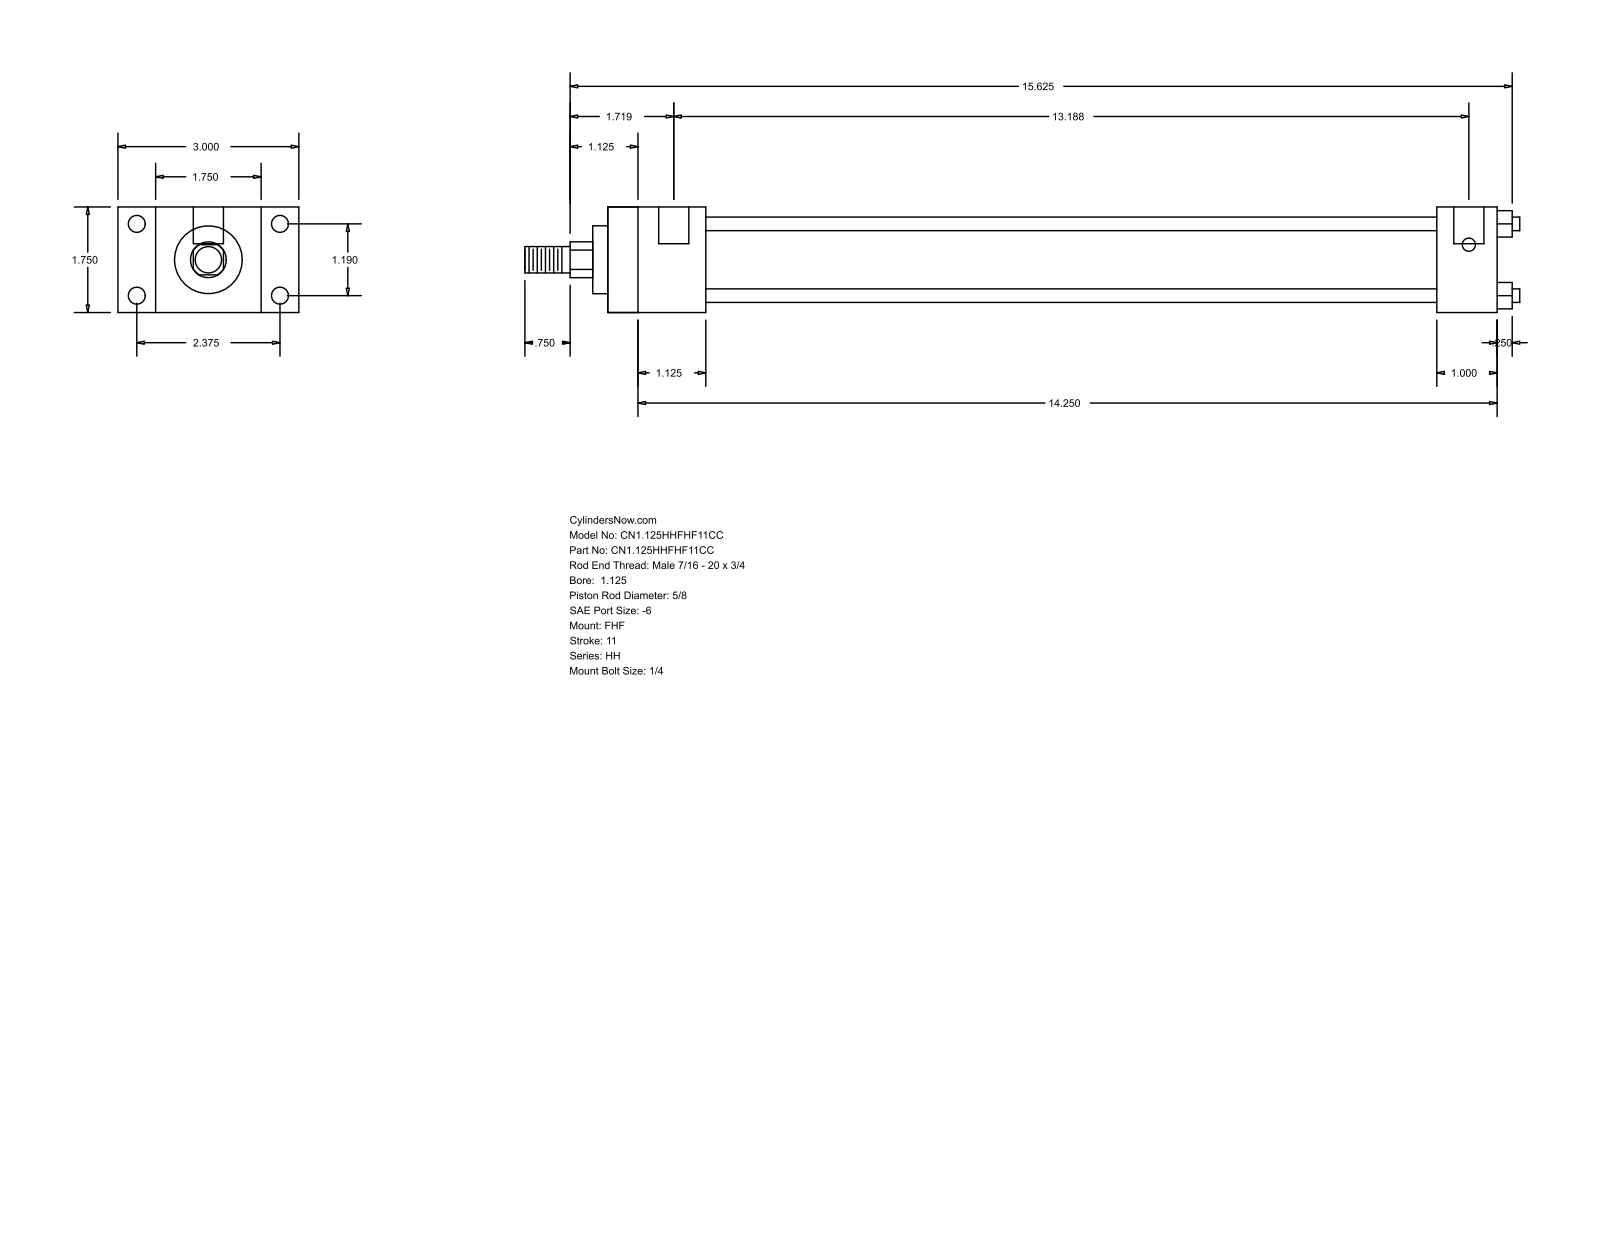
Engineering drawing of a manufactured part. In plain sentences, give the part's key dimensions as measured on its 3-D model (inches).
The part is named "HH_FHF__0112_0.625". Its 3-D file was written by "GSSL Pune (CONFIG_CONTROL_DESIGN)". It is 0 solids with 88 faces: 60 planar, 28 cylindrical and 0 other. Overall it measures 16.5 by 3 by 1.75 inches. Round holes: 4 of diameter 0.219, 4 of diameter 0.281, 2 of diameter 0.5. Round bosses or shafts: 4 of diameter 0.225, 1 of diameter 1.375, 1 of diameter 1.125, 1 of diameter 0.625, 1 of diameter 0.437. Partial cylindrical surfaces (rounded edges, fillets, slot ends): 1 of radius 0.297. The main face-to-face distances are 1.75, 0.625, 2.375, 1.625, 3, 14.75, 13.125, 1, 13.75, 12.125. The hole center spacings are 1.19, 2.375, 2.656, 13.063, 0.125, 13.187.
